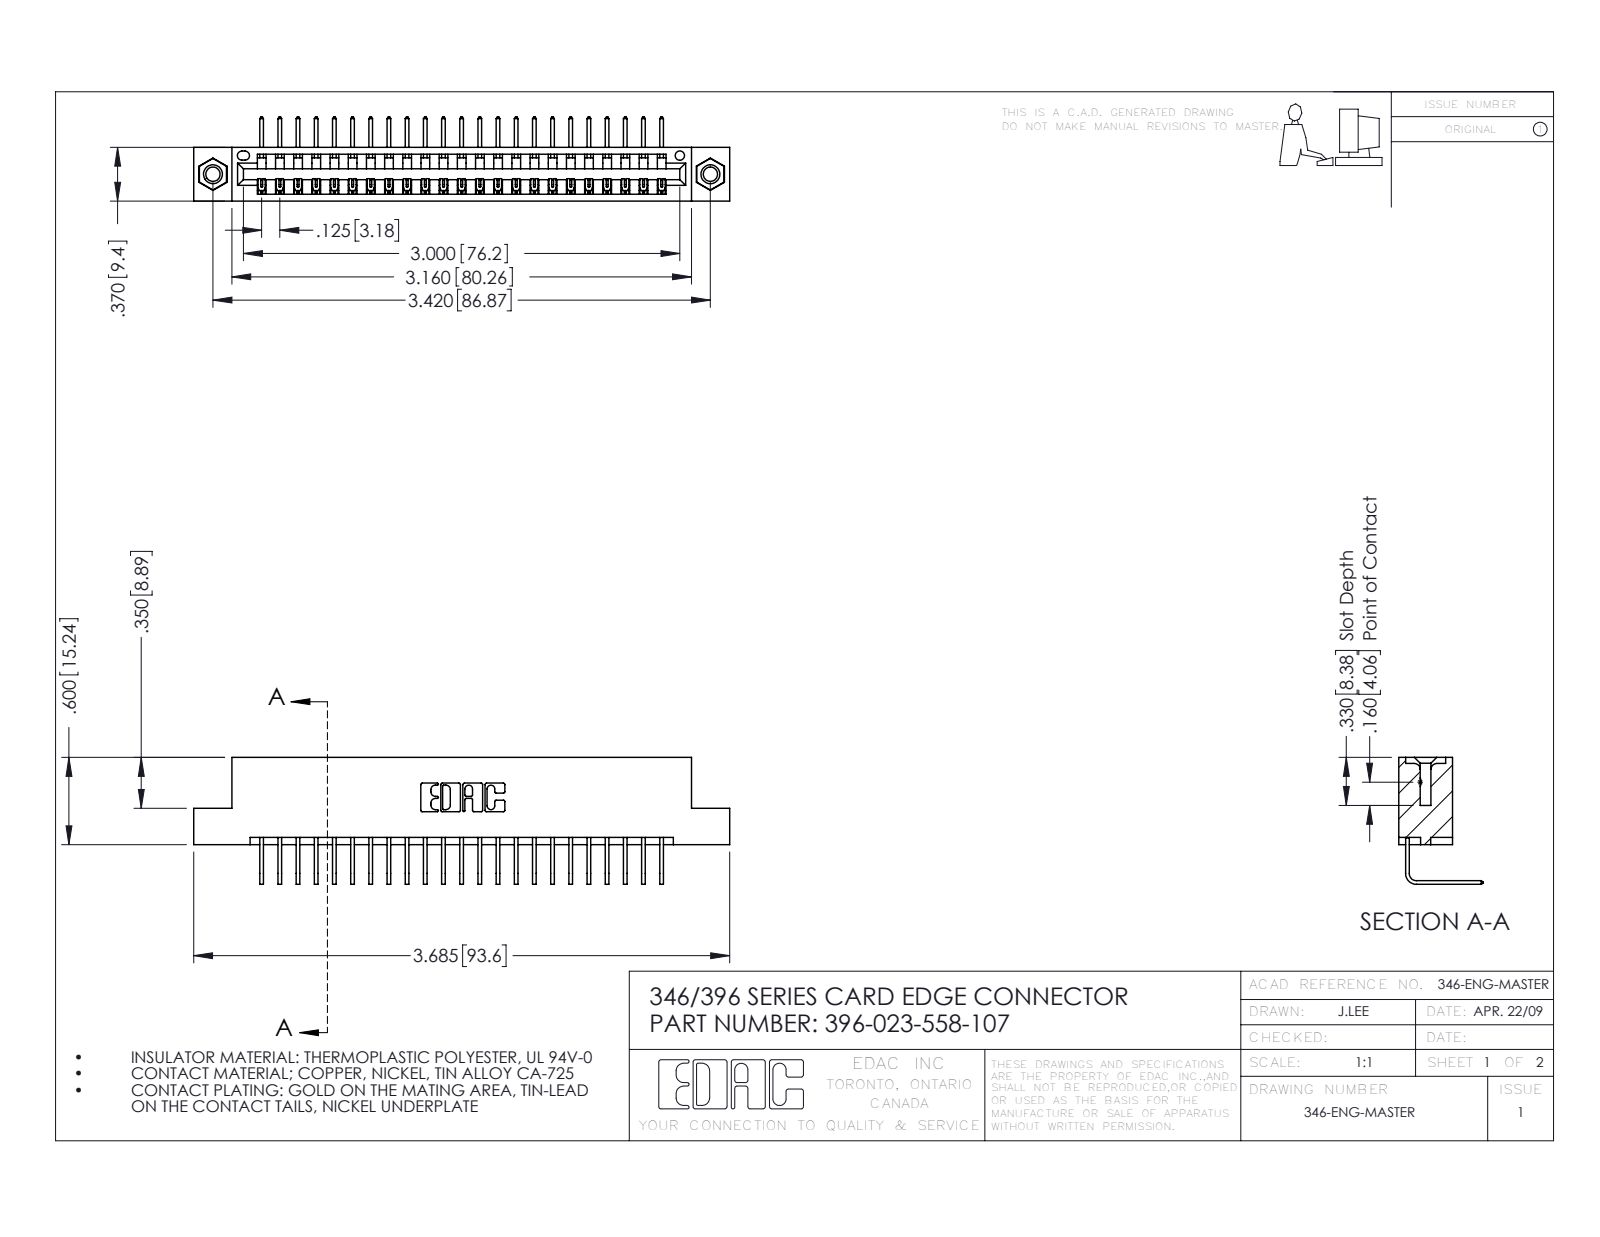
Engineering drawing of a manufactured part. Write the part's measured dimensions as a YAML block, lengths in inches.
part_name: "345-292-001_558 Tail - 2; 345-250-001_345-250-005-103; 396-023-558-107; 346 Part_Flush Mounting Lugs - 0.156 Dia-TI"
step_written_by: "SolidWorks 2016 (CONFIG_CONTROL_DESIGN)"
units: inches
bodies: {solids: 26, faces: 1562, planar: 1074, cylindrical: 472, other: 16}
overall_size: [3.685, 0.873, 0.58]
volume: 0.543
surface_area: 17.67
round_holes:
  - {diameter: 0.098, count: 2}
  - {diameter: 0.125, count: 2}
  - {diameter: 0.156, count: 2}
  - {diameter: 0.064, count: 1}
round_bosses_or_shafts:
  - {diameter: 0.155, count: 2}
partial_cylinders:
  - {radius: 0.006, count: 46}
  - {radius: 0.01, count: 22}
  - {radius: 0.007, count: 6}
  - {radius: 0.031, count: 6}
  - {radius: 0.026, count: 3}
  - {radius: 0.031, count: 2}
  - {radius: 0.04, count: 2}
  - {radius: 0.014, count: 1}
face_to_face_distances: [0.322, 0.048, 0.25, 0.37, 0.298, 0.025, 0.072, 0.148, 0.222, 0.1]
hole_center_spacings: [0.246, 3.212, 3.42]
